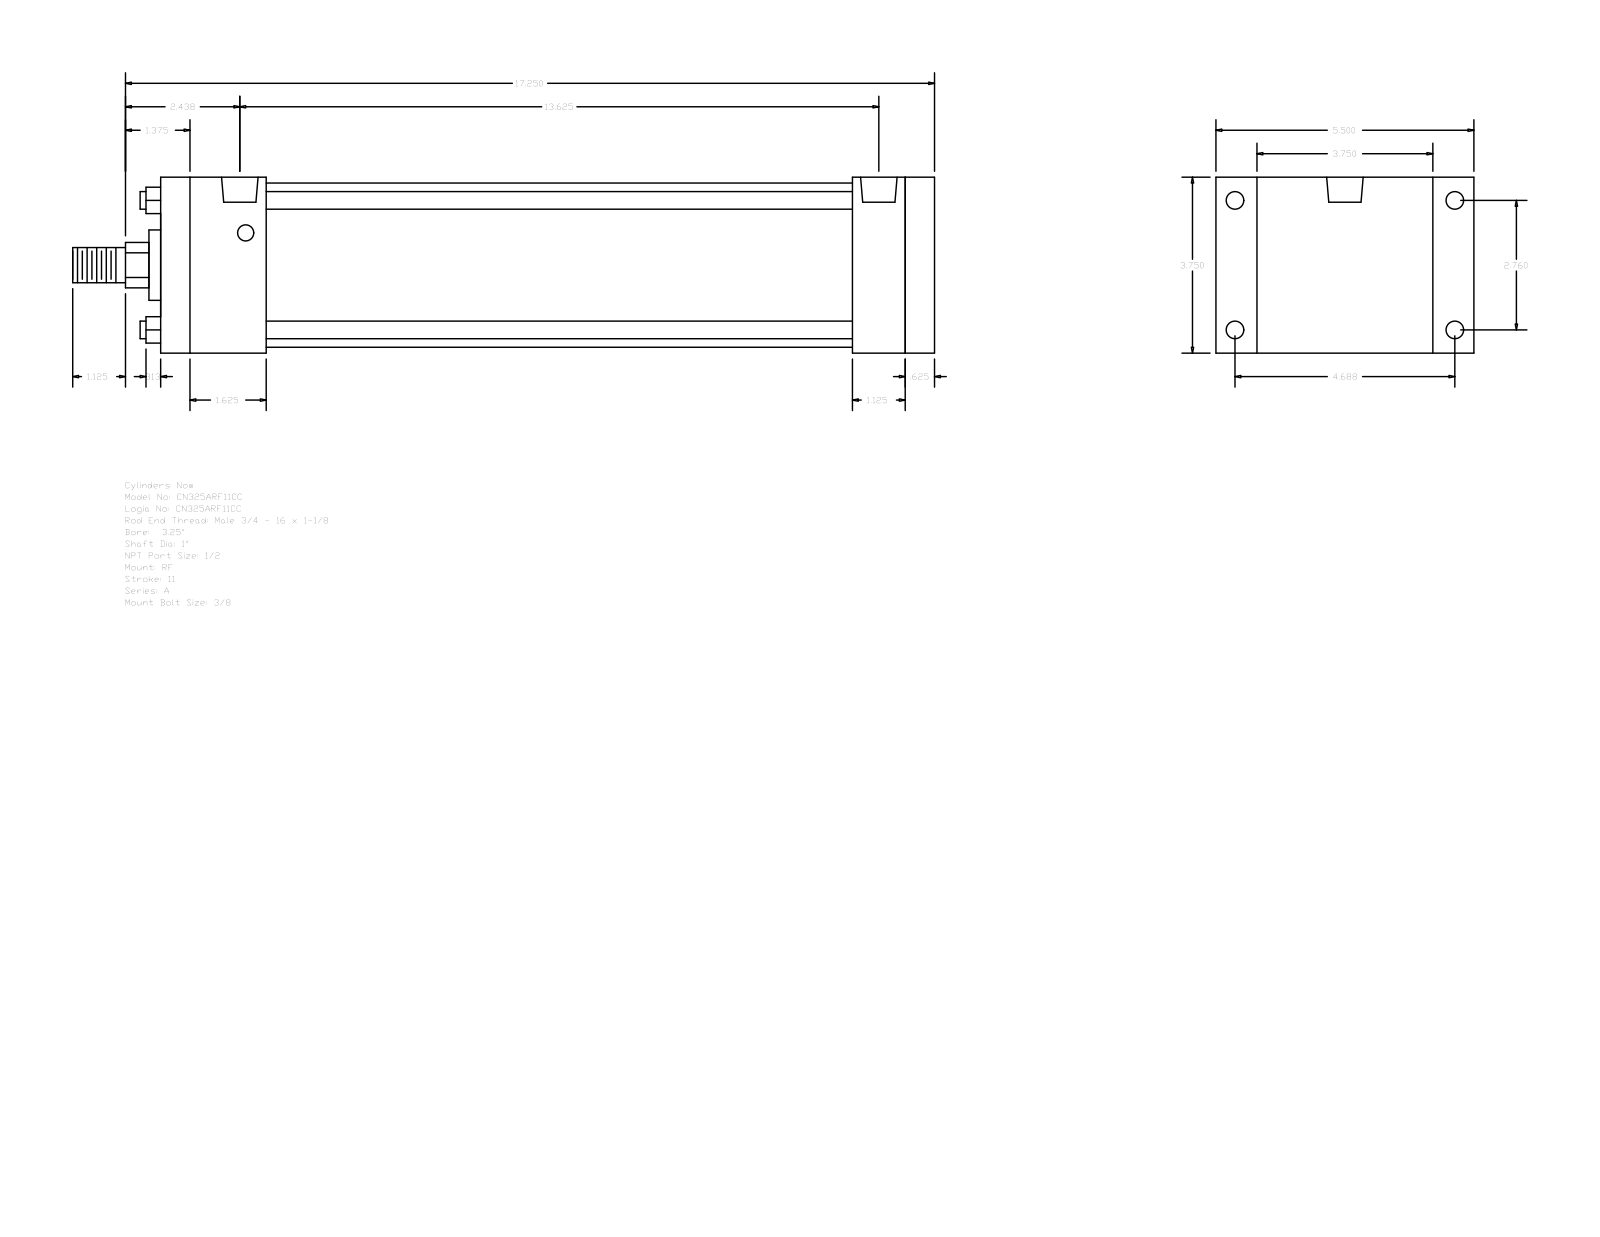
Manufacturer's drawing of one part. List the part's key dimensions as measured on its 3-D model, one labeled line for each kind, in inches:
Part name (STEP PRODUCT): A_RF__0325_1
STEP written by: GSSL Pune (CONFIG_CONTROL_DESIGN)
Units: inches
Bodies: 0 solids, 92 faces (64 planar, 28 cylindrical, 0 other)
Overall size (bounding box): 18.375 × 5.5 × 3.75
Round holes (diameter × count): ⌀0.344 ×4, ⌀0.375 ×4, ⌀0.778 ×2
Round bosses / shafts (diameter × count): ⌀0.375 ×4, ⌀3.5 ×1, ⌀1.5 ×1, ⌀1 ×1, ⌀0.75 ×1
Partial cylindrical surfaces — rounded edges, fillets, slot ends (radius × count): R0.484 ×1
Main face-to-face distances: 3.75, 16.5, 15.875, 0.625, 0.875, 4.625, 1.125, 14.75, 1.75, 2.25
Hole centre spacings: 0.125, 2.76, 4.687, 5.439, 13.375, 13.5, 13.625
